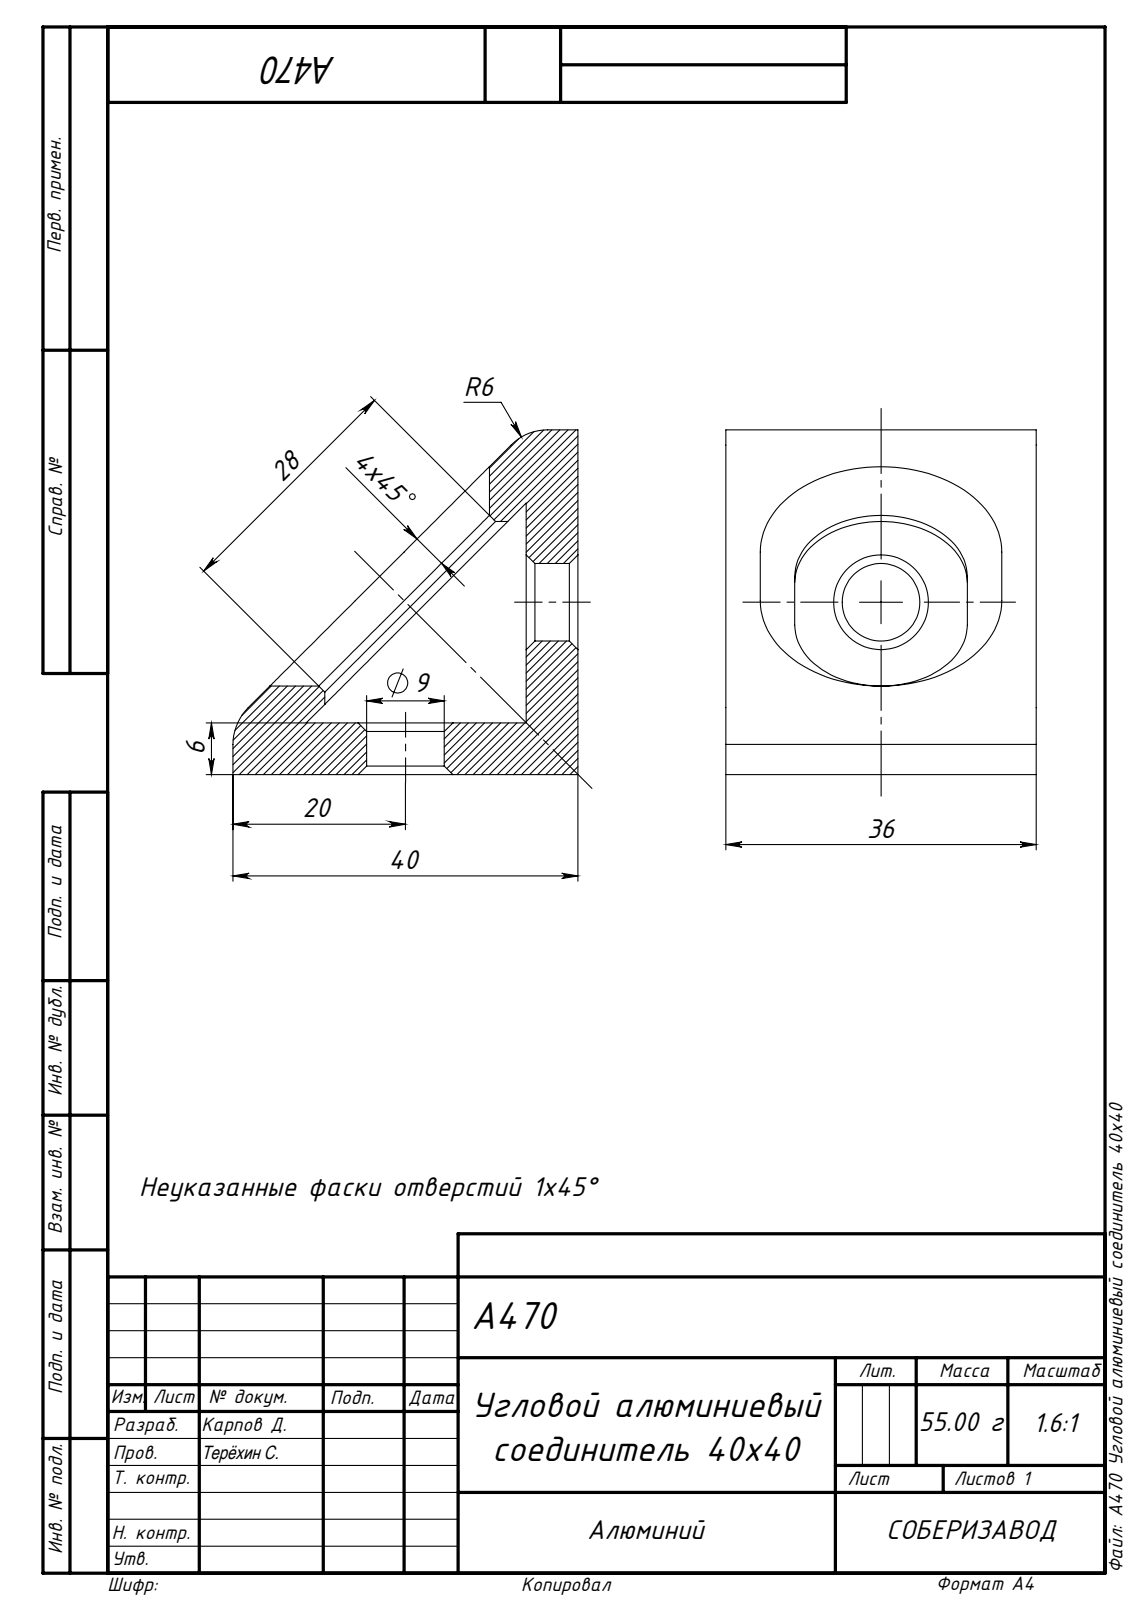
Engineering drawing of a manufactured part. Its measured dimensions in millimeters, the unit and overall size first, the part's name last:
Units: millimetres
Overall size (bounding box): 40 × 40 × 36
Round holes (diameter × count): ⌀9 ×2
Partial cylindrical surfaces — rounded edges, fillets, slot ends (radius × count): R6 ×2, R10 ×2
Main face-to-face distances: 6, 36, 40, 34, 13.43, 8, 28, 20
Volume: 20 611 mm³ · Surface area: 8 890 mm²
Bodies: 1 solid, 39 faces (16 planar, 9 cylindrical, 14 other)
Part name (STEP PRODUCT): A470 Угловой алюминиевый соединитель 40х40
STEP written by: SolidWorks 2021 (AUTOMOTIVE_DESIGN)
